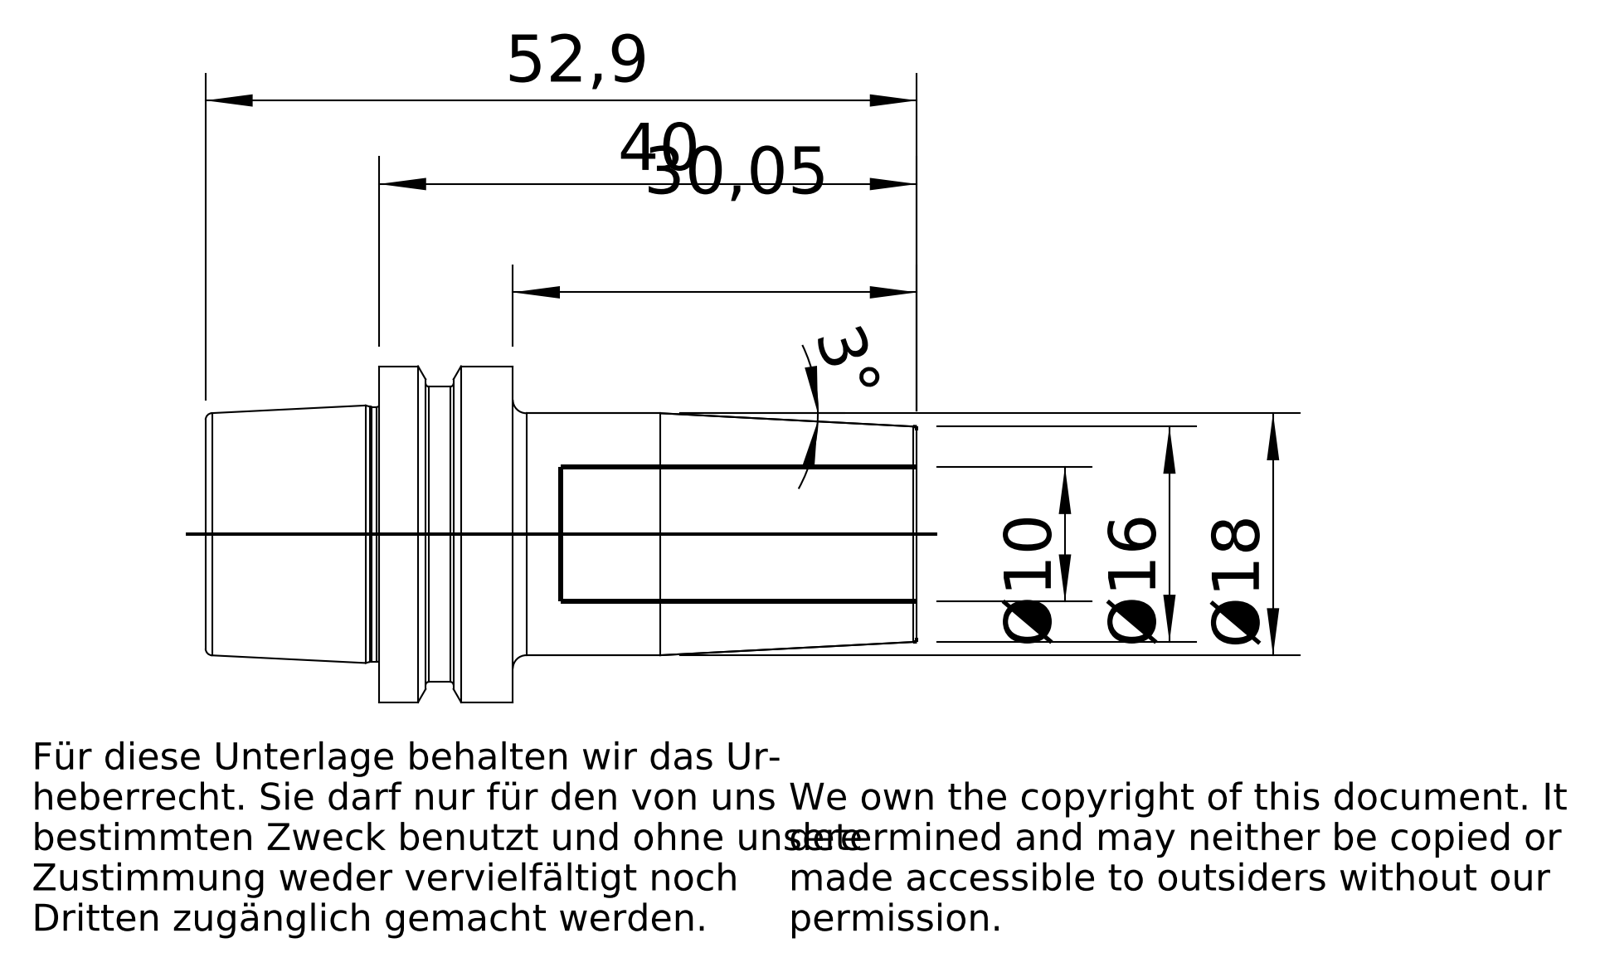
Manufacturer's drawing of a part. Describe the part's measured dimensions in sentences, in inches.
The part is named "E25-185-10". Its 3-D file was written by "PRO/ENGINEER BY PARAMETRIC TECHNOLOGY CORPORATION, 2010430 (CONFIG_CONTROL_DESIGN)". It is 1 solid with 62 faces: 8 planar, 18 cylindrical and 36 other. Overall it measures 2.083 by 0.984 by 0.984 inches. Its volume is 0.602 cubic inches and its surface area 9.173 square inches. Round holes: 1 of diameter 0.394, 1 of diameter 0.553, 1 of diameter 0.648. Round bosses or shafts: 1 of diameter 0.984, 1 of diameter 0.864, 1 of diameter 0.746, 1 of diameter 0.709. The main face-to-face distances are 0.157, 0.234, 0.392, 1.575, 1.341, 1.183, 0.531, 0.297, 0.14, 1.043.
